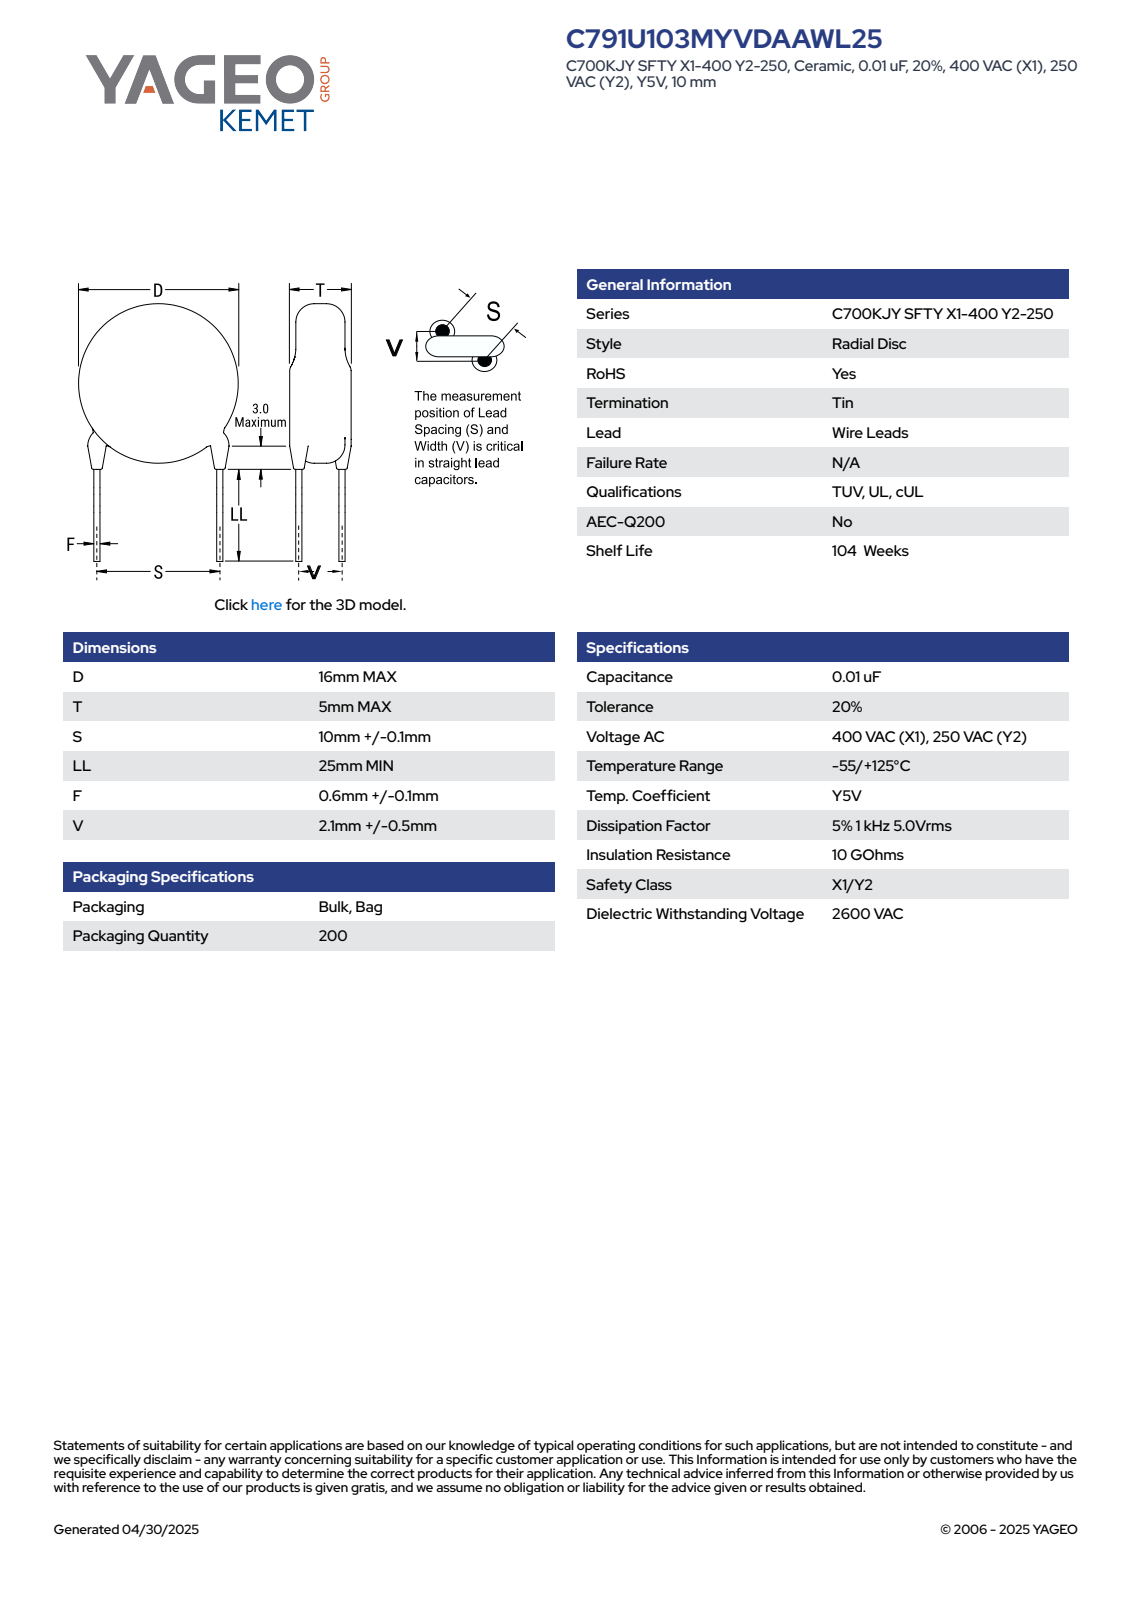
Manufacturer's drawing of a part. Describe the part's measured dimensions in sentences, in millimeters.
The part is named "CCD_KST_16X5_D16T5S10LL25F0.7V2.1". Its 3-D file was written by "SolidWorks 2021 (AUTOMOTIVE_DESIGN)". It is 4 solids with 77 faces: 63 planar, 10 cylindrical and 4 other. Overall it measures 41 by 16 by 5 millimeters. Its volume is 1 008 cubic millimeters and its surface area 753 square millimeters. Round bosses or shafts: 2 of diameter 1.2, 2 of diameter 0.7, 1 of diameter 16. The main face-to-face distances are 5, 25, 34.39, 9.39, 32.55, 7.55, 1.84, 0.5, 0.35, 1.49.
